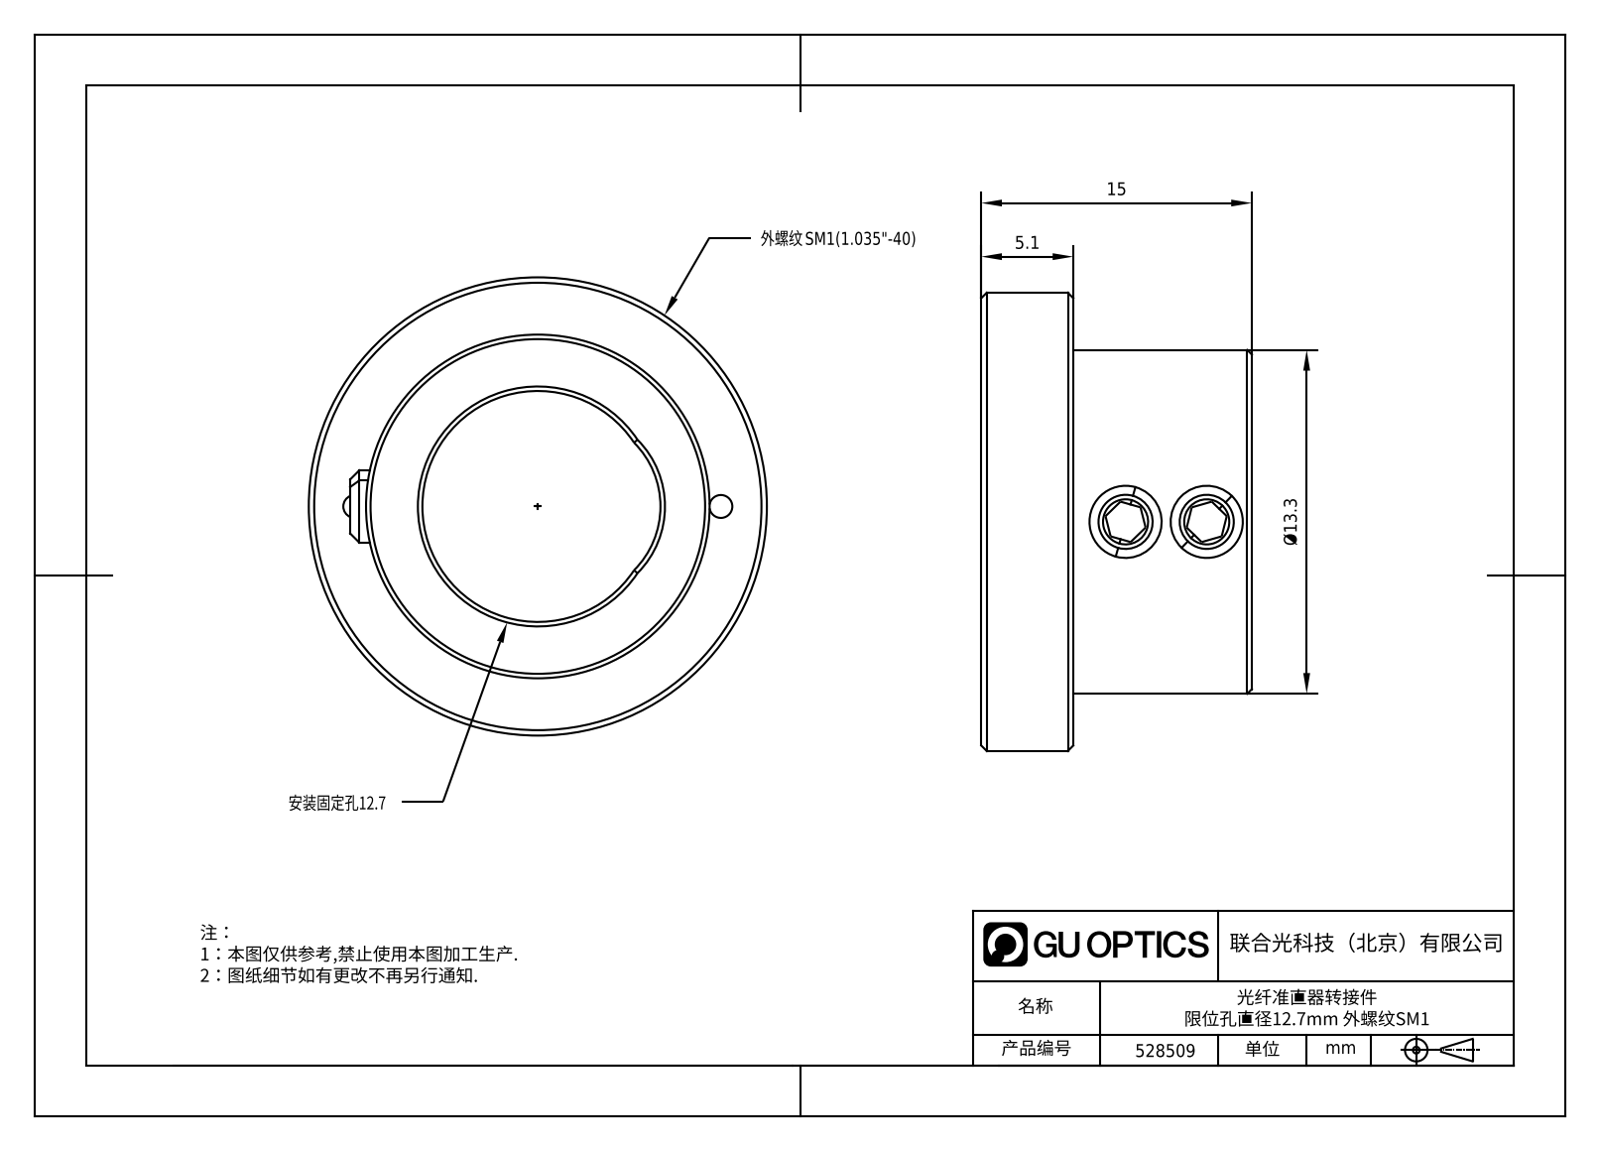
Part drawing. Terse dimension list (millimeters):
name: 30.8.8-14，M4尼龙头顶丝，A_30.8.56-LNJ4*3
written by: SolidWorks 2021 (CONFIG_CONTROL_DESIGN)
unit: mm
bodies: 3 solids, 85 faces (27 planar, 28 cylindrical, 30 other)
size: 25.4 × 25.4 × 15
volume: 3 449 mm³; area: 2 500 mm²
holes: 4× ⌀1.27, 2× ⌀3.3, 1× ⌀12.8
bosses: 2× ⌀4, 2× ⌀3, 1× ⌀25.4, 1× ⌀19.05
rounds: 1× R5
face distances: 5.1, 15, 9.9, 3, 1.27, 3.83, 2, 4, 1, 11.17
hole spacings: 10.15, 14.35, 20.3, 4.5
